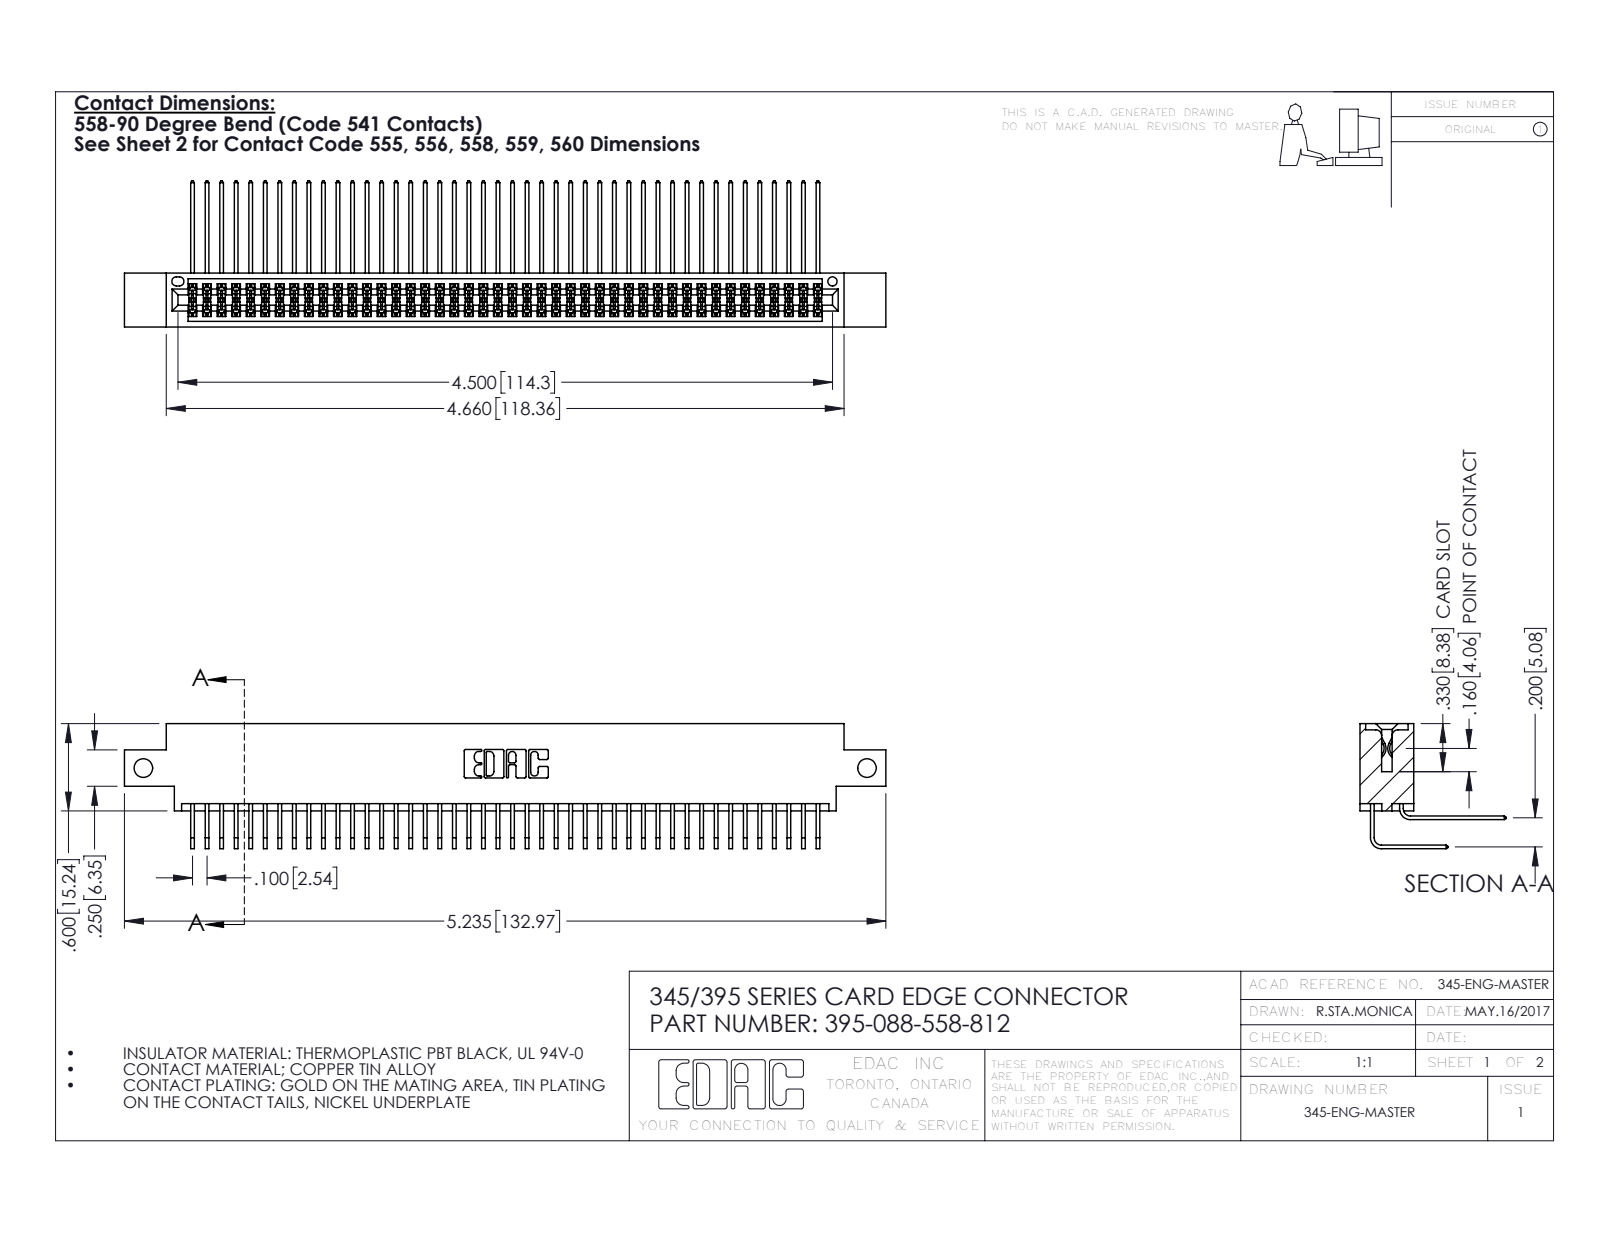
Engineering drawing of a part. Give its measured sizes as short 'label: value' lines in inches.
name: 345-292-001_558 Tail - 2; 345-292-001_558 559 Tail - 1; 395-088-558-812; 345 Part_0.170 Offset - Side Mount
written by: SolidWorks 2016 (CONFIG_CONTROL_DESIGN)
unit: in
bodies: 89 solids, 4706 faces (3164 planar, 1542 cylindrical, 0 other)
size: 5.235 × 1.005 × 0.859
volume: 0.808 in³; area: 34.11 in²
holes: 2× ⌀0.128, 1× ⌀0.064
rounds: 133× R0.006, 22× R0.01, 6× R0.007, 6× R0.031, 3× R0.026, 2× R0.014, 2× R0.019, 2× R0.022
face distances: 0.072, 0.298, 0.2, 0.37, 0.098, 0.272, 0.025, 0.225, 0.175, 0.025
hole spacings: 4.975
